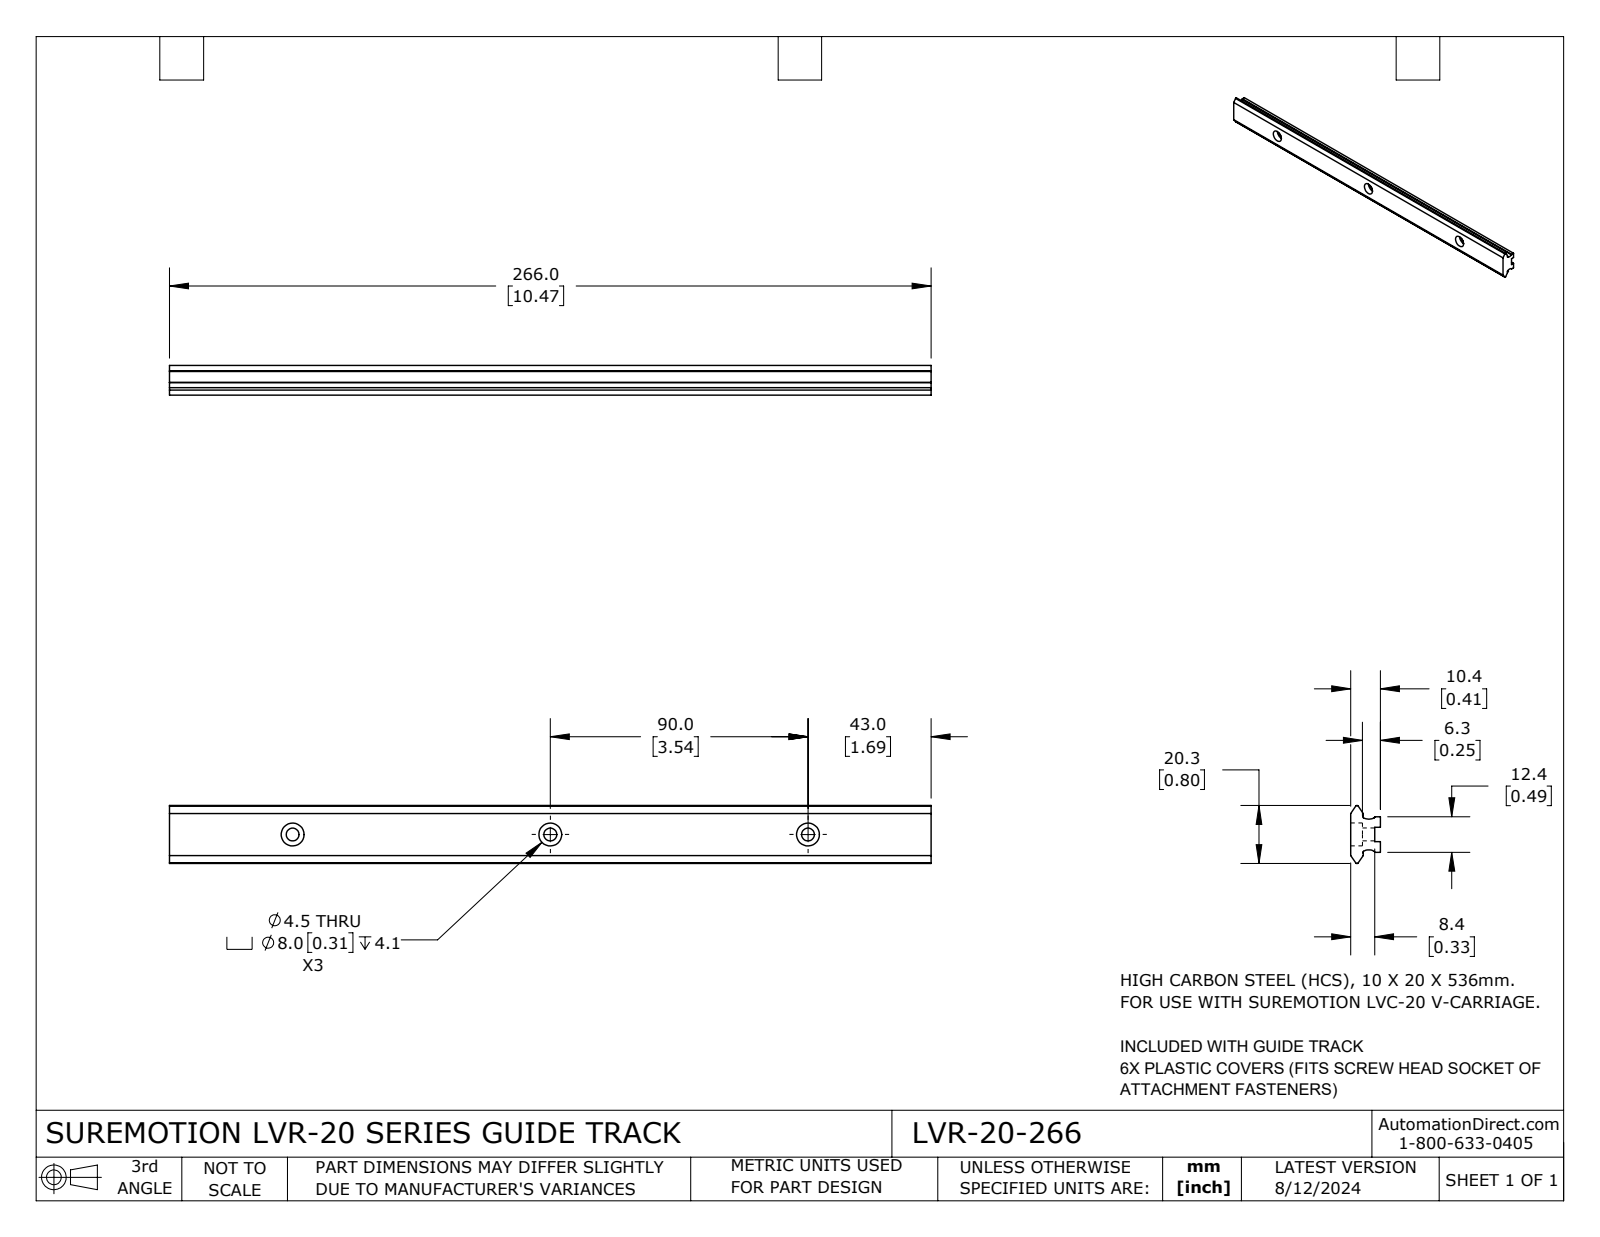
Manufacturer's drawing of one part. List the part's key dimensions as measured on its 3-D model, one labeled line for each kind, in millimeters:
Part name (STEP PRODUCT): LVR-20-266
STEP written by: SolidWorks 2023 (CONFIG_CONTROL_DESIGN)
Units: millimetres
Bodies: 1 solid, 41 faces (19 planar, 22 cylindrical, 0 other)
Overall size (bounding box): 266 × 20.27 × 10.41
Volume: 35 743 mm³ · Surface area: 17 030 mm²
Round holes (diameter × count): ⌀4.5 ×3, ⌀8 ×3
Partial cylindrical surfaces — rounded edges, fillets, slot ends (radius × count): R0.4 ×4, R0.5 ×2, R3.84 ×2
Main face-to-face distances: 10.41, 2, 8.41, 3.7, 8.7, 12.06, 12.05, 5, 12.4, 5.99
Hole centre spacings: 90, 180
